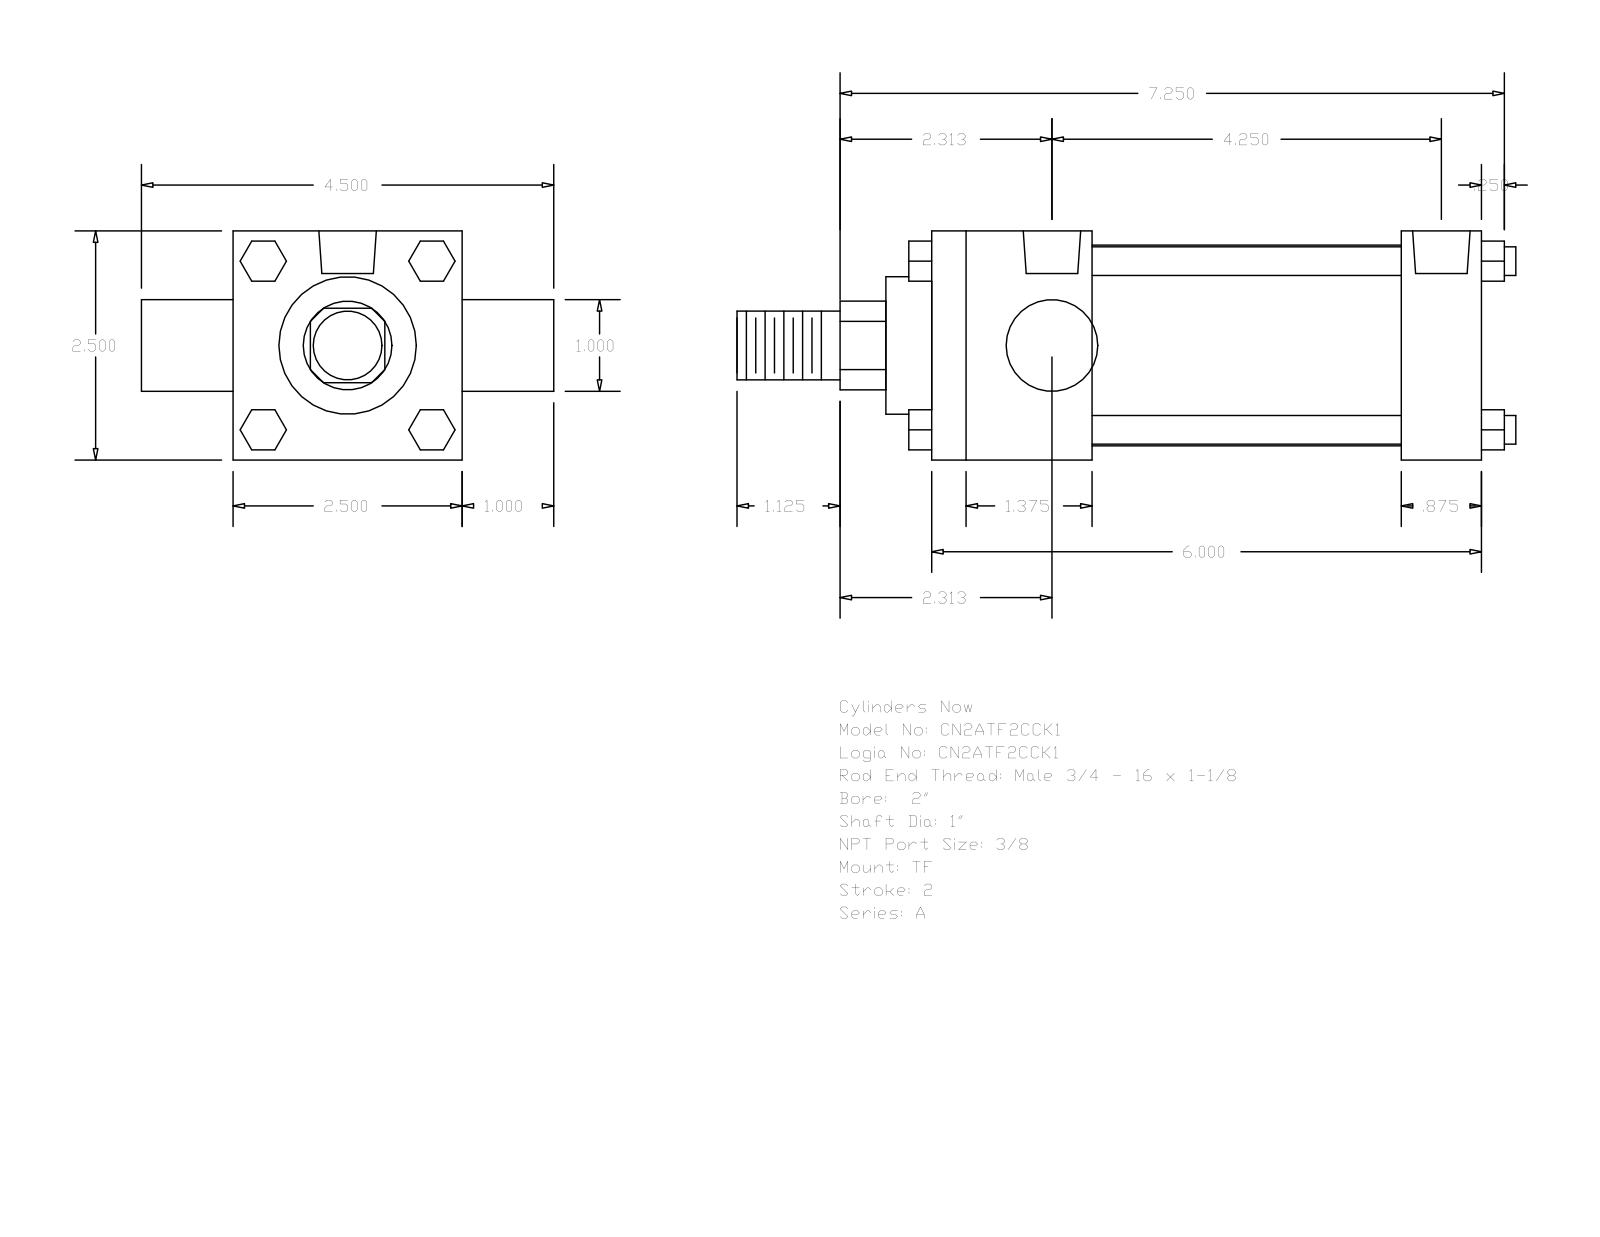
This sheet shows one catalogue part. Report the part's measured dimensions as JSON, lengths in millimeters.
{"part_name": "A_TF__0200_1", "step_written_by": "GSSL Pune (CONFIG_CONTROL_DESIGN)", "units": "millimeters", "bodies": {"solids": 0, "faces": 120, "planar": 92, "cylindrical": 28, "other": 0}, "overall_size": [215.9, 114.3, 63.5], "round_holes": [[5.56, 3], [15.93, 2]], "round_bosses_or_shafts": [[7.94, 4], [25.4, 2], [55.63, 1], [38.1, 1], [19.05, 1]], "partial_cylinders_radius": [[12.29, 1]], "face_to_face_distances": [63.5, 152.4, 44.45, 130.17, 85.72, 107.95, 22.23, 25.4, 88.9, 165.1], "hole_center_spacings": [1.59, 3.98, 102.38, 103.97, 106.36, 107.95]}
